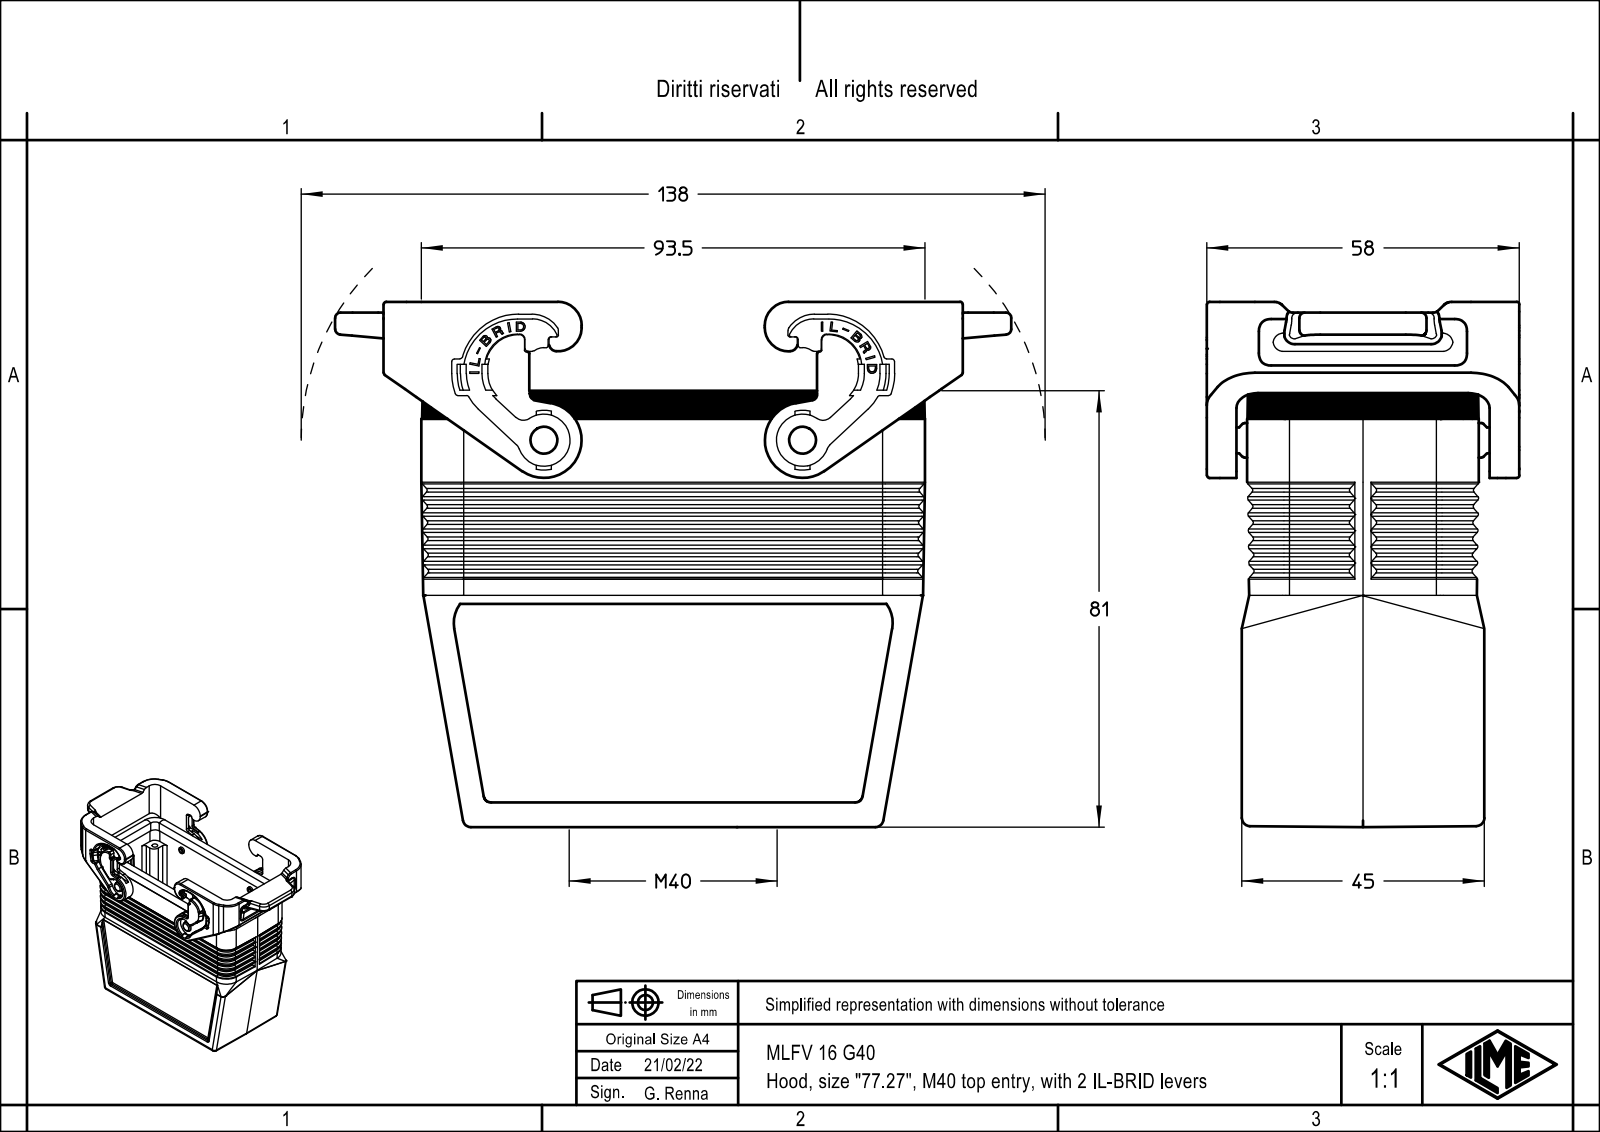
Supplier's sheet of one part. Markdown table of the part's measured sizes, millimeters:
| quantity | value |
| --- | --- |
| part name | MLFV_16_G40 |
| STEP written by | Creo Elements/Direct Modeling 20.1B 02-Apr-2019 (C) Parametric Technology GmbH (AUTOMOTIVE_DESIGN) |
| units | millimeters |
| bodies | 1 solid, 1601 faces (1031 planar, 391 cylindrical, 179 other) |
| overall size | 125.5 × 97.45 × 58 |
| volume | 115 569 mm³ |
| surface area | 60 316 mm² |
| round holes (diameter × count) | 2.75 × 4, 38.6 × 1 |
| round bosses / shafts (diameter × count) | 6.8 × 2, 4.8 × 2 |
| partial cylindrical surfaces (radius × count) | 0.5 × 104, 1 × 46, 3 × 20, 7 × 16, 0.33 × 15, 1.5 × 14, 0.3 × 8, 2 × 8 |
| main face-to-face distances | 39.25, 3.75, 2, 5.75, 1, 43, 4.75, 45, 41.25, 35.5 |
| hole center spacings | 41.03, 27, 77.5, 82.07 |
